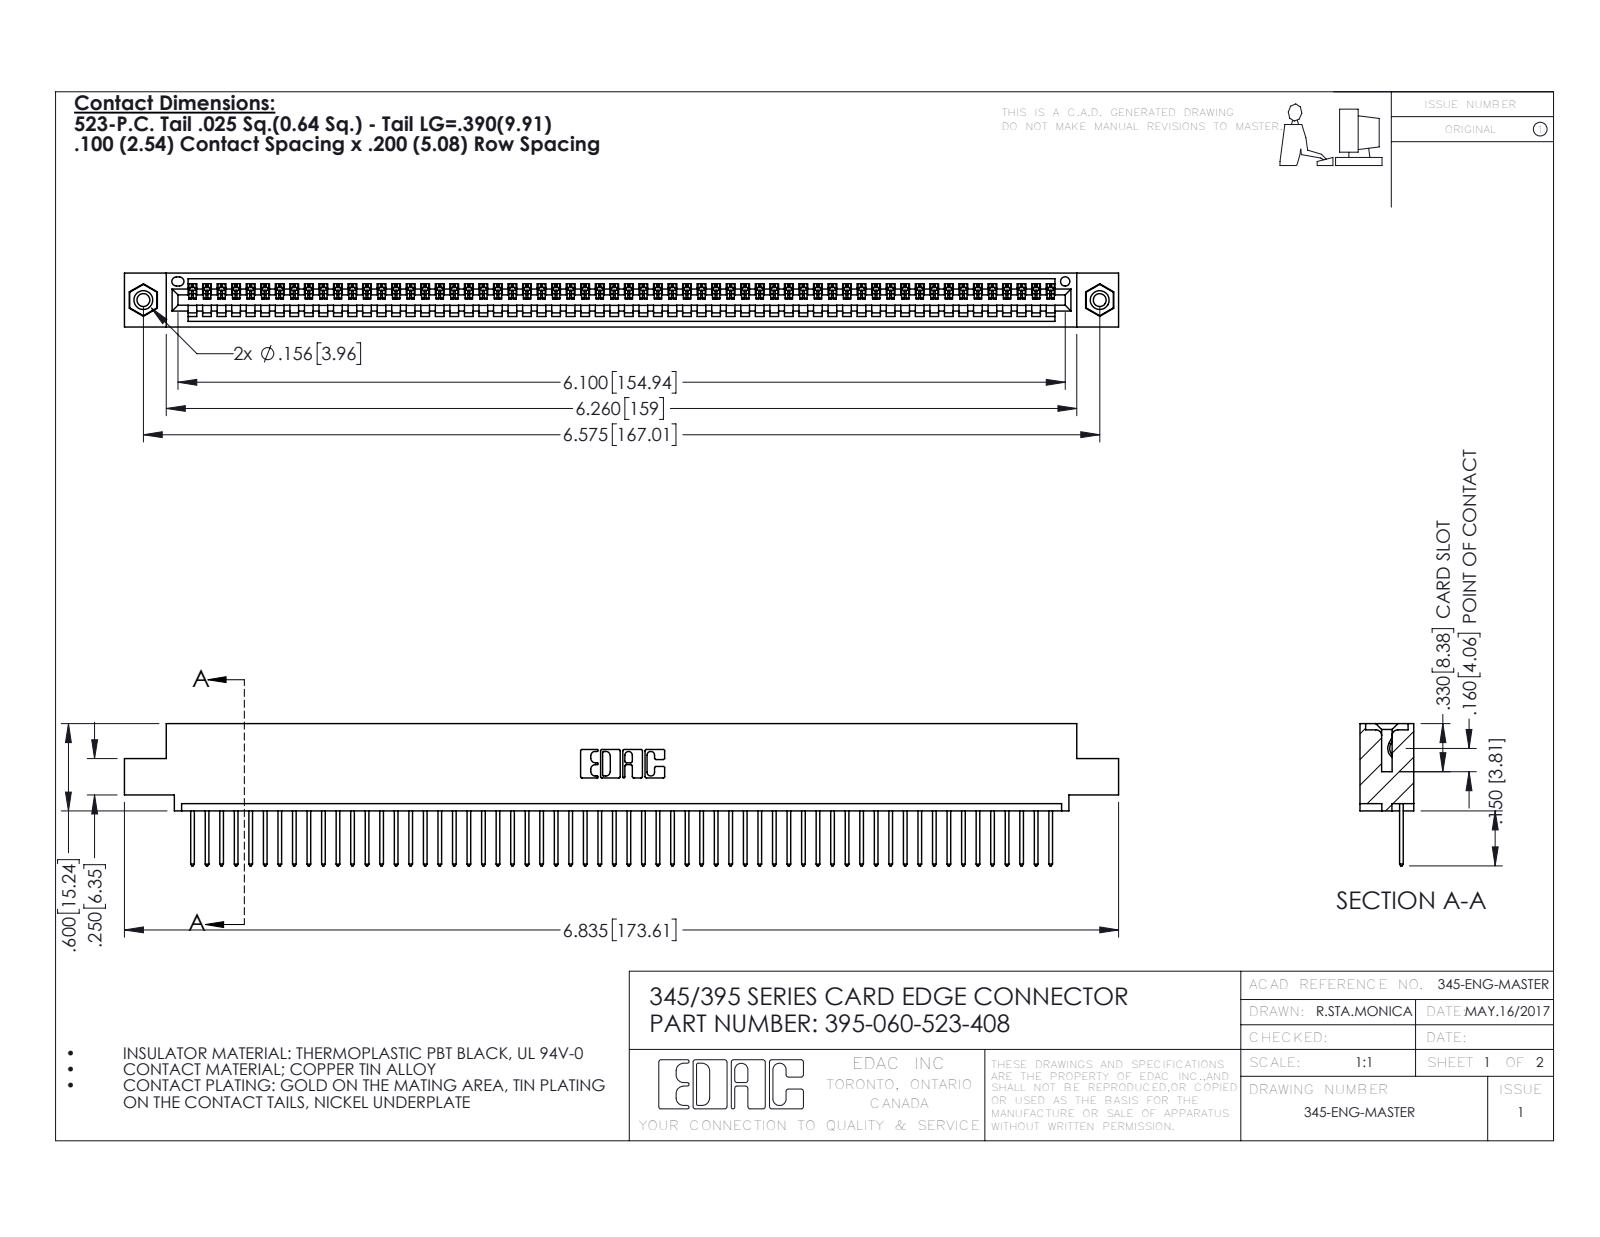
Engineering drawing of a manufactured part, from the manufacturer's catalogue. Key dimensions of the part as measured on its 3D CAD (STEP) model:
Part name (STEP PRODUCT): 345-250-001_345-250-003-102; 345-292-001_345-293-123; 345 Part_0.110 Offset - 0.156 Dia-TI; 395-060-523-408
STEP written by: SolidWorks 2016 (CONFIG_CONTROL_DESIGN)
Units: inches
Bodies: 63 solids, 3670 faces (2516 planar, 1138 cylindrical, 16 other)
Overall size (bounding box): 6.835 × 0.977 × 0.37
Volume: 1.009 in³ · Surface area: 34.69 in²
Round holes (diameter × count): ⌀0.089 ×2, ⌀0.125 ×2, ⌀0.156 ×2, ⌀0.064 ×1
Round bosses / shafts (diameter × count): ⌀0.155 ×2
Partial cylindrical surfaces — rounded edges, fillets, slot ends (radius × count): R0.006 ×120, R0.01 ×120, R0.01 ×22, R0.007 ×6, R0.031 ×6, R0.026 ×3, R0.031 ×2, R0.04 ×2
Main face-to-face distances: 0.072, 0.298, 0.37, 0.098, 0.272, 0.025, 0.2, 0.225, 0.149, 0.072
Hole centre spacings: 0.27, 6.339, 6.575
